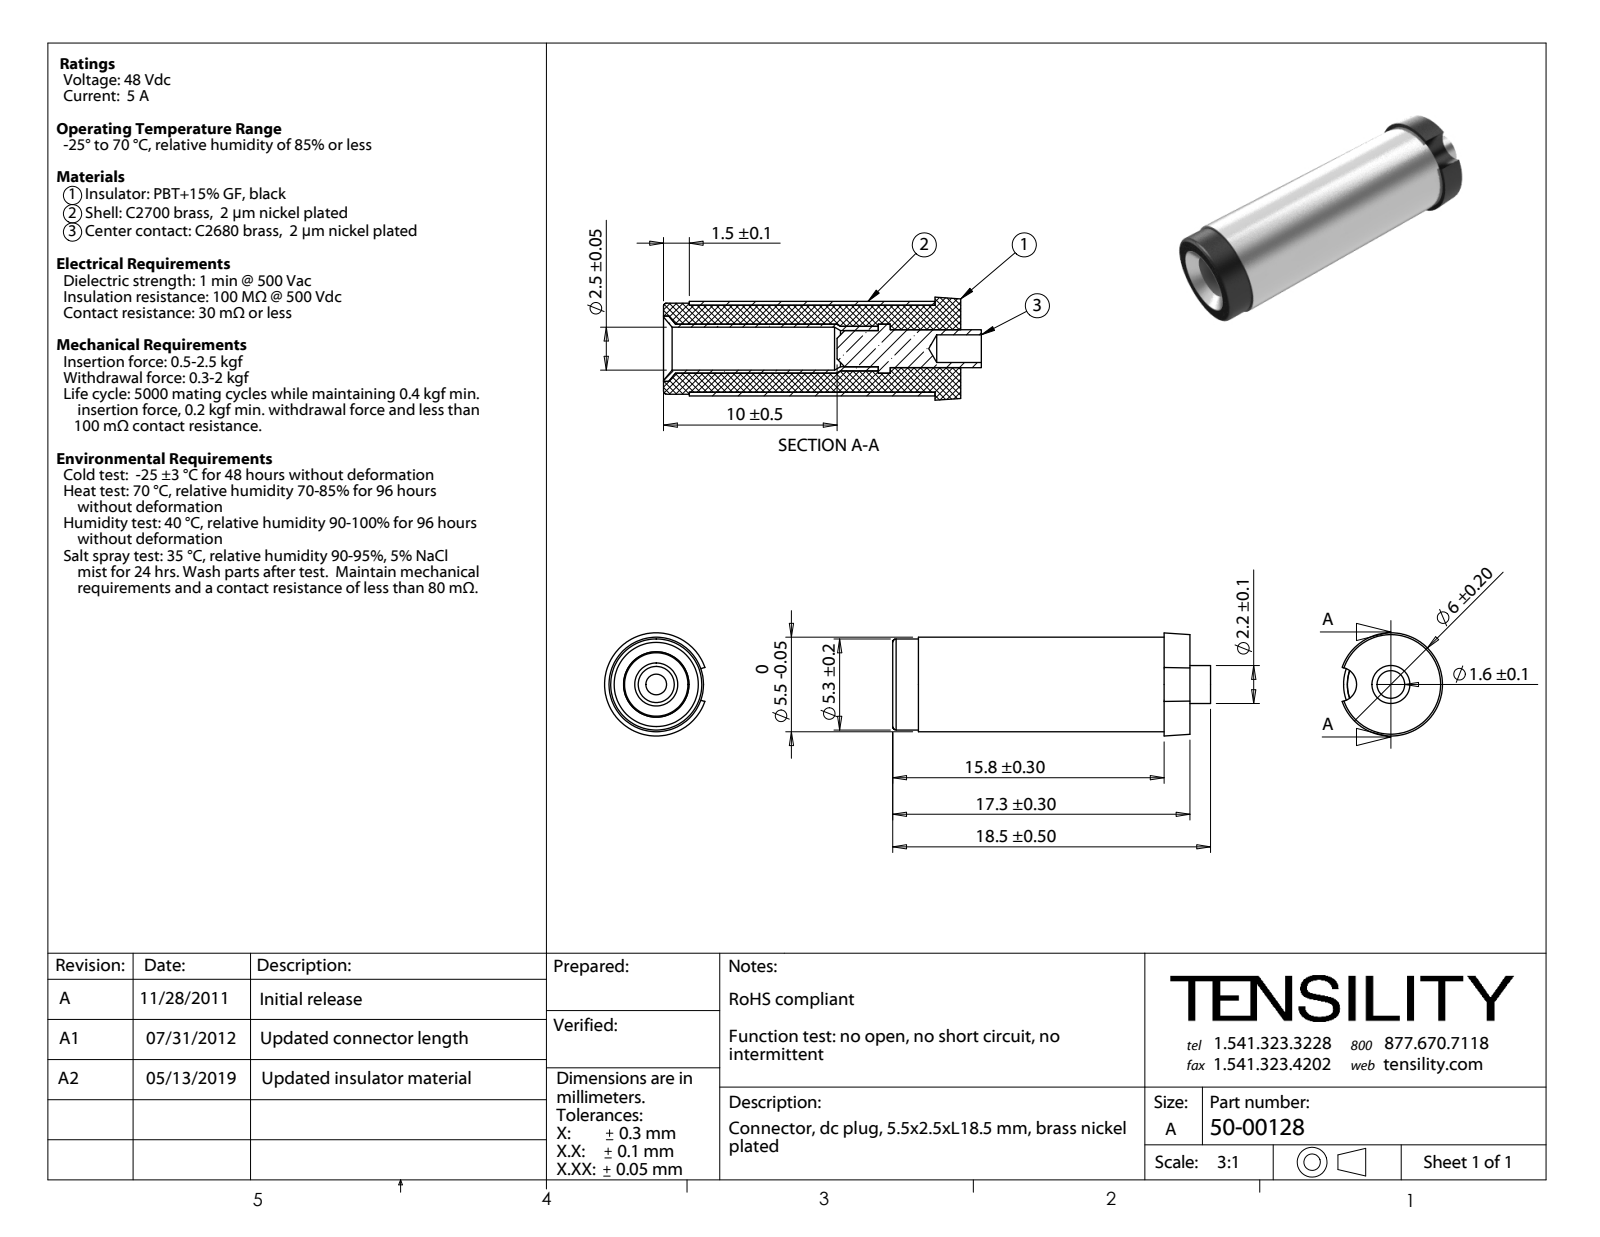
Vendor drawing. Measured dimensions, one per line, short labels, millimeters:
name: 5525C185-DI03; 5525C185-DH02; 5525C185-ET04; 50-00128_revA2 (+1 more)
written by: SolidWorks 2015 (CONFIG_CONTROL_DESIGN)
unit: mm
bodies: 4 solids, 72 faces (15 planar, 38 cylindrical, 19 other)
size: 18.5 × 6 × 5.83
volume: 359 mm³; area: 1 255 mm²
holes: 1× ⌀1.61, 1× ⌀2.1, 1× ⌀2.2, 1× ⌀2.5, 1× ⌀2.6, 1× ⌀2.85, 1× ⌀3.8, 1× ⌀5.06
bosses: 1× ⌀5.5, 1× ⌀5.3, 1× ⌀2.86, 1× ⌀2.21, 1× ⌀2.11
rounds: 1× R1
face distances: 1.5, 15.8, 17.3, 12.5, 3.3, 4.8, 11, 14.3, 13.2, 11.7
